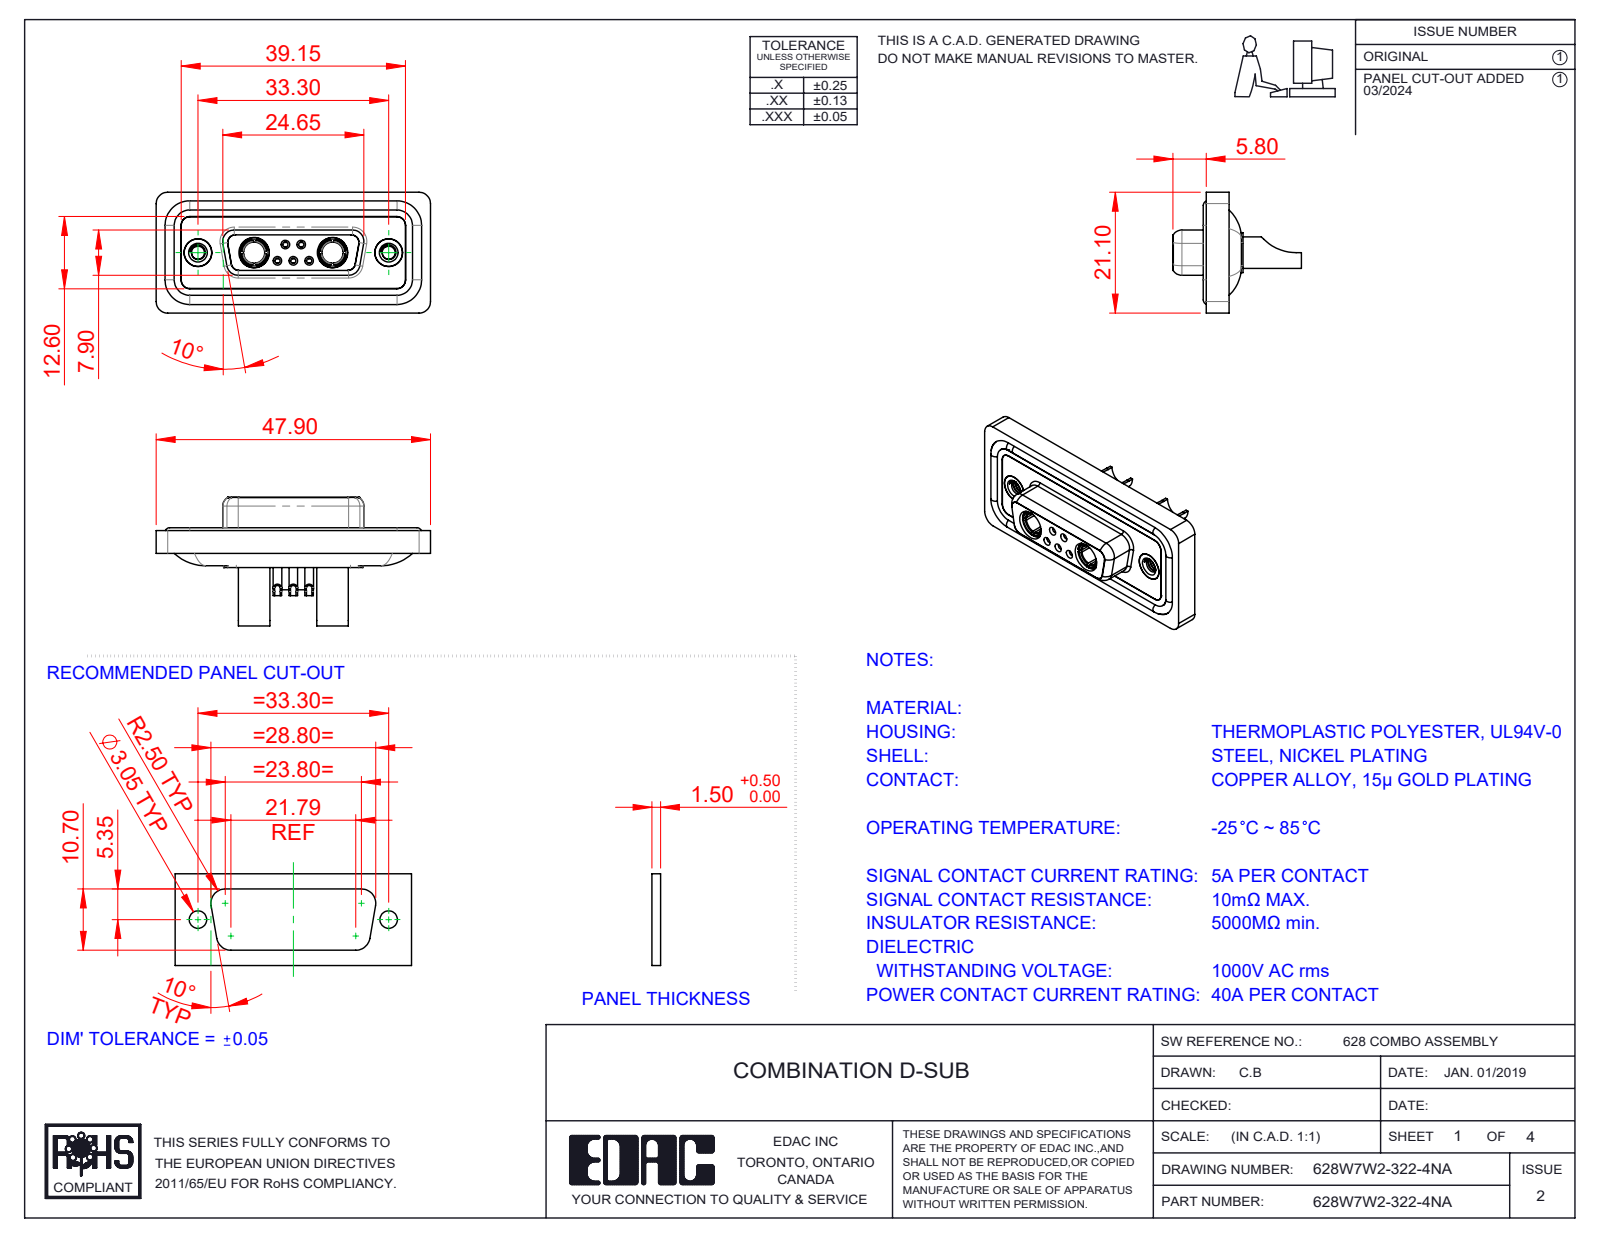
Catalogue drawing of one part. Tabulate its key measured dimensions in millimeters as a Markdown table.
| quantity | value |
| --- | --- |
| part name | 628Combo Contact Row 2_22; 628Combo Waterproof Housing_15 Contacts; Power Socket_40A SC; 628Combo Contact Row 1_22 (+5 more) |
| STEP written by | SolidWorks 2023 (CONFIG_CONTROL_DESIGN) |
| units | millimeters |
| bodies | 16 solids, 813 faces (252 planar, 343 cylindrical, 218 other) |
| overall size | 47.9 × 22.45 × 21.1 |
| volume | 6 169 mm³ |
| surface area | 10 217 mm² |
| round holes (diameter × count) | 0.9 × 5, 1 × 5, 1.1 × 5, 1.5 × 5, 2 × 5, 4.85 × 4, 1.6 × 3, 1.7 × 2, 2.26 × 2, 3.7 × 2, 4 × 2, 4.05 × 2 |
| round bosses / shafts (diameter × count) | 1.6 × 6, 2.2 × 5, 5.5 × 2, 5.2 × 2, 4.96 × 2, 4.95 × 2, 4.8 × 2, 4.75 × 2 |
| partial cylindrical surfaces (radius × count) | 1.5 × 22, 2 × 20, 1.35 × 12, 1.6 × 8, 1 × 6, 0.25 × 4, 0.5 × 4, 0.6 × 4 |
| main face-to-face distances | 0.4, 1.6, 1.8, 0.5, 2.9, 1.1, 7.45, 5.65, 6.6, 7.05 |
| hole center spacings | 3.16, 2.77, 9.8, 23.5, 4.31, 4.33, 5.03, 5.04 |
